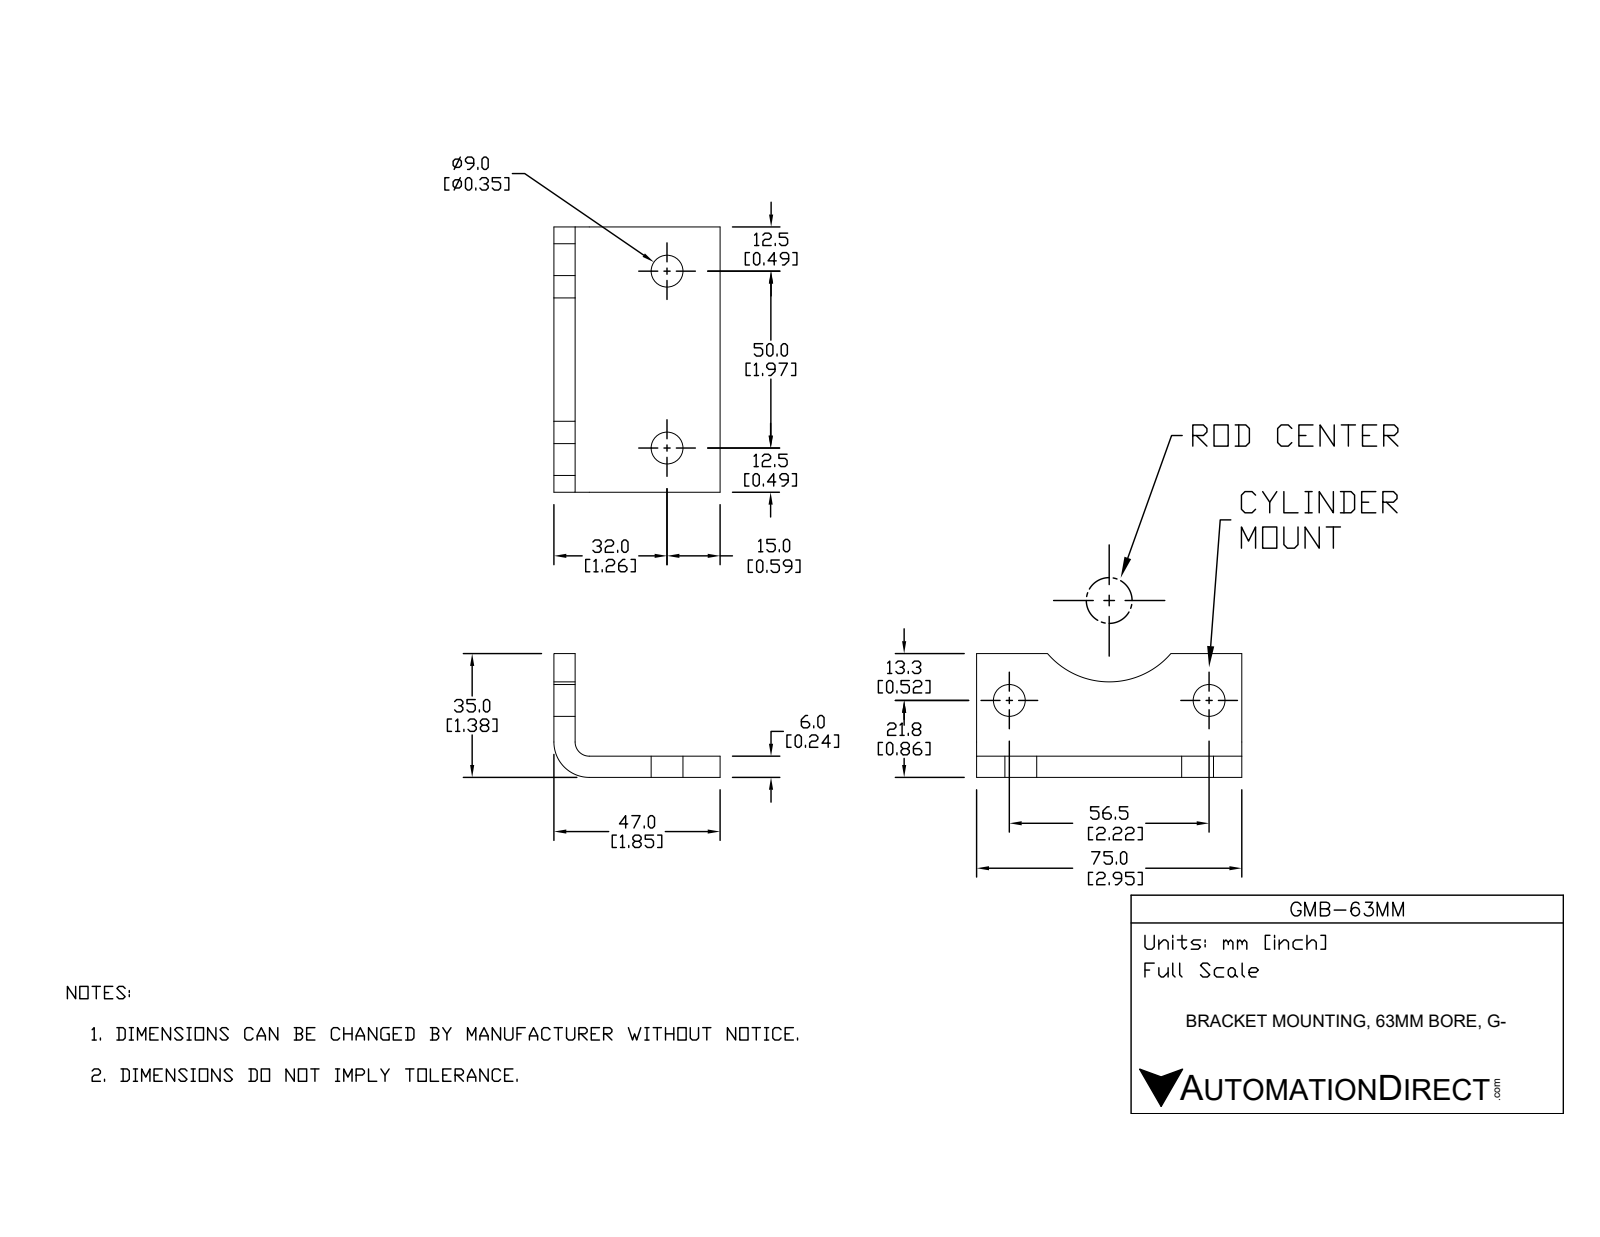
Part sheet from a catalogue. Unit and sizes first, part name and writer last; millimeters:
Units: millimetres
Overall size (bounding box): 75 × 47 × 35
Round holes (diameter × count): ⌀9 ×4
Partial cylindrical surfaces — rounded edges, fillets, slot ends (radius × count): R1 ×1, R7 ×1, R23 ×1
Main face-to-face distances: 6, 47, 41, 75, 35, 29
Hole centre spacings: 50, 56.5
Volume: 30 739 mm³ · Surface area: 12 745 mm²
Bodies: 1 solid, 24 faces (13 planar, 11 cylindrical, 0 other)
Part name (STEP PRODUCT): GMB-63MM
STEP written by: SolidWorks 2017 (AUTOMOTIVE_DESIGN)
